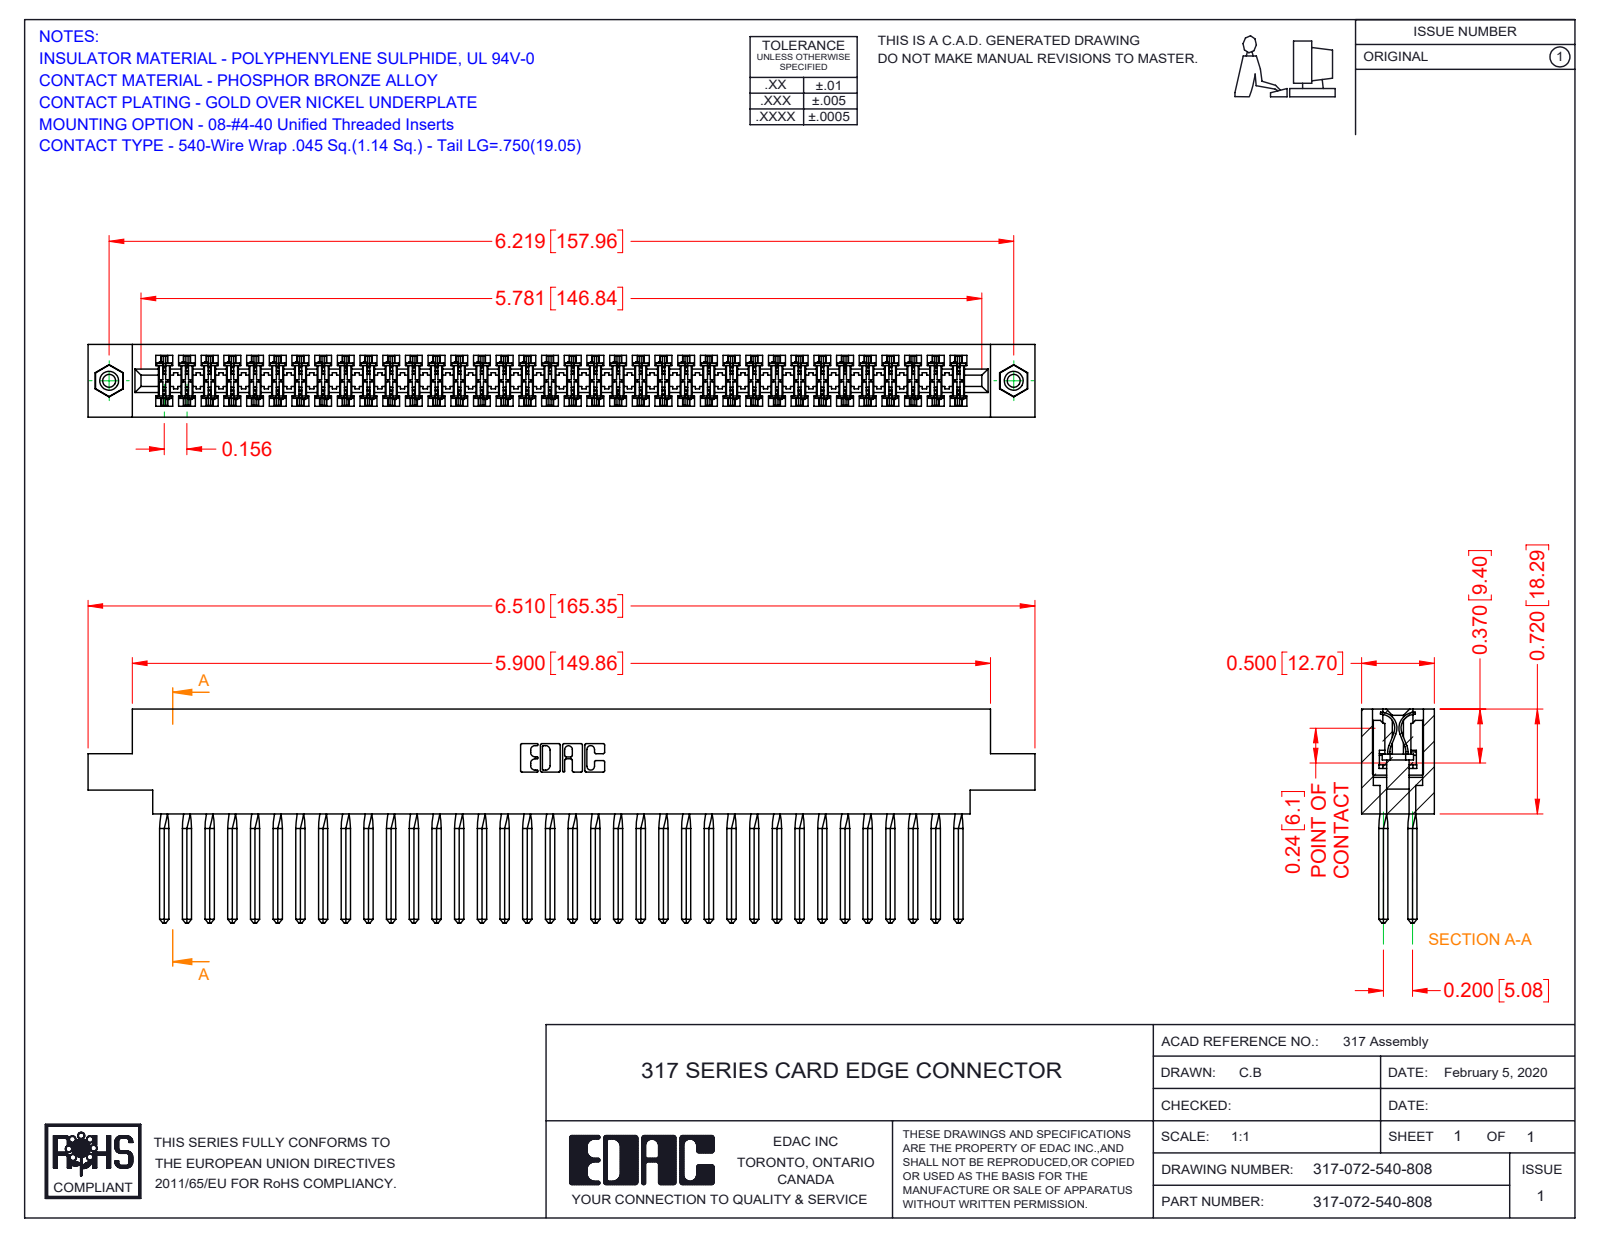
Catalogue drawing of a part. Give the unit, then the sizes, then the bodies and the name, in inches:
Units: inches
Overall size (bounding box): 6.51 × 1.47 × 0.5
Round holes (diameter × count): ⌀0.089 ×2, ⌀0.125 ×2, ⌀0.156 ×2
Round bosses / shafts (diameter × count): ⌀0.155 ×2
Partial cylindrical surfaces — rounded edges, fillets, slot ends (radius × count): R0.015 ×144, R0.01 ×22, R0.007 ×6, R0.031 ×6, R0.026 ×3, R0.095 ×2, R0.1 ×2, R0.11 ×2
Main face-to-face distances: 0.5, 0.075, 0.425, 0.35, 0.195, 0.11, 0.094, 0.2, 0.115, 0.131
Hole centre spacings: 6.219
Volume: 1.681 in³ · Surface area: 63.33 in²
Bodies: 75 solids, 6570 faces (5346 planar, 920 cylindrical, 304 other)
Part name (STEP PRODUCT): 317-290-001_540; 317-072-540-808; 345-250-001_345-250-003-102; 317 Part_.156 Dia - TI
STEP written by: SolidWorks 2016 (CONFIG_CONTROL_DESIGN)
